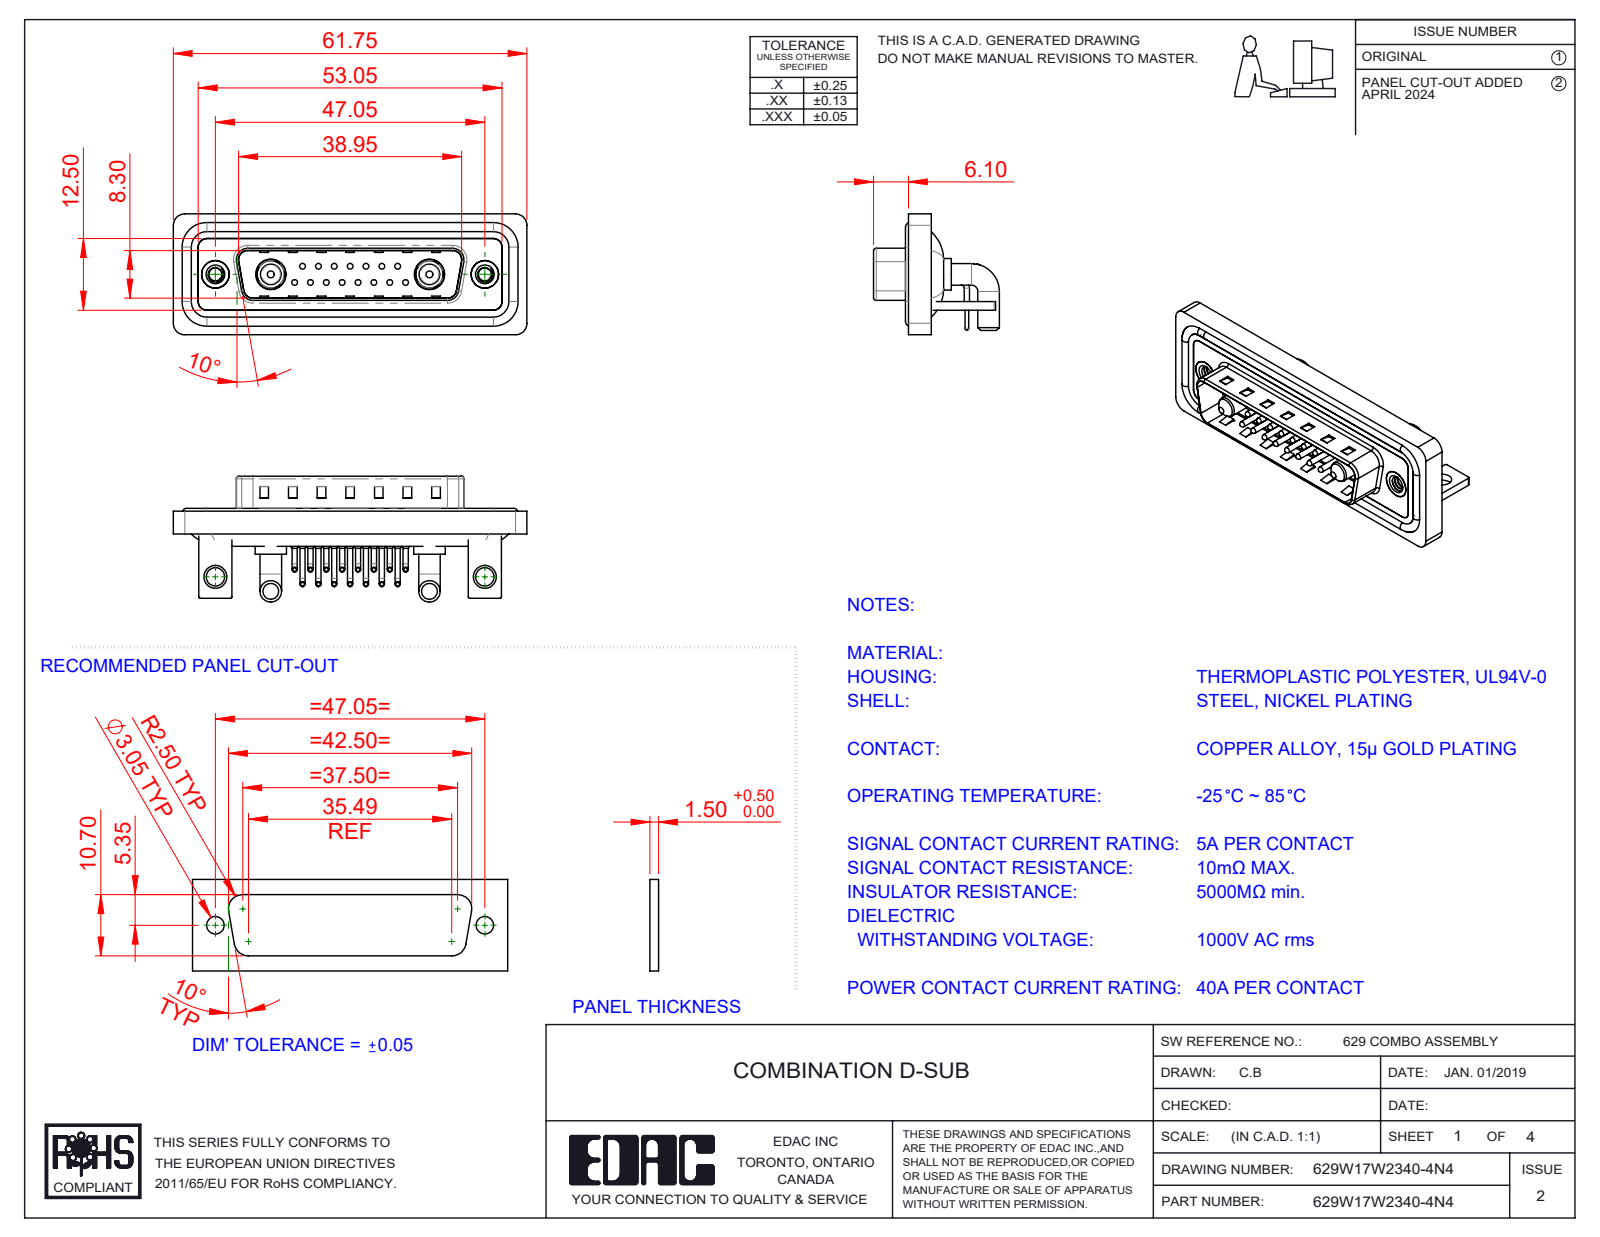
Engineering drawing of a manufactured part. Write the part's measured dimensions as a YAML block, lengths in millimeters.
part_name: "629W17W2340-4N4; 629Combo Shell Front_25 Contacts; 629Combo Waterproof Housing_25 Contacts; 629Combo Contact Row 2 (+6 more)"
step_written_by: "SolidWorks 2023 (CONFIG_CONTROL_DESIGN)"
units: millimeters
bodies: {solids: 28, faces: 2259, planar: 1209, cylindrical: 788, other: 262}
overall_size: [61.75, 21.98, 21.1]
volume: 7936
surface_area: 13276
round_holes:
  - {diameter: 0.75, count: 15}
  - {diameter: 1.6, count: 15}
  - {diameter: 2, count: 15}
  - {diameter: 2.26, count: 2}
  - {diameter: 3.2, count: 2}
  - {diameter: 4, count: 2}
  - {diameter: 4.8, count: 2}
  - {diameter: 4.85, count: 2}
  - {diameter: 5, count: 2}
  - {diameter: 5.3, count: 2}
round_bosses_or_shafts:
  - {diameter: 0.9, count: 30}
  - {diameter: 1.5, count: 15}
  - {diameter: 1, count: 15}
  - {diameter: 0.65, count: 15}
  - {diameter: 3.75, count: 4}
  - {diameter: 1.6, count: 4}
  - {diameter: 5.5, count: 2}
  - {diameter: 5.2, count: 2}
partial_cylinders:
  - {radius: 2, count: 19}
  - {radius: 1.5, count: 18}
  - {radius: 0.25, count: 16}
  - {radius: 1.01, count: 15}
  - {radius: 0.5, count: 9}
  - {radius: 1.6, count: 8}
  - {radius: 0.6, count: 4}
  - {radius: 0.65, count: 4}
face_to_face_distances: [0.4, 0.8, 2.1, 1.5, 2.9, 1.1, 4.1, 1.6, 4.5, 3.7]
hole_center_spacings: [3.16, 2.77, 5.54, 8.31, 5.04, 7.49, 11.08, 5.03]
